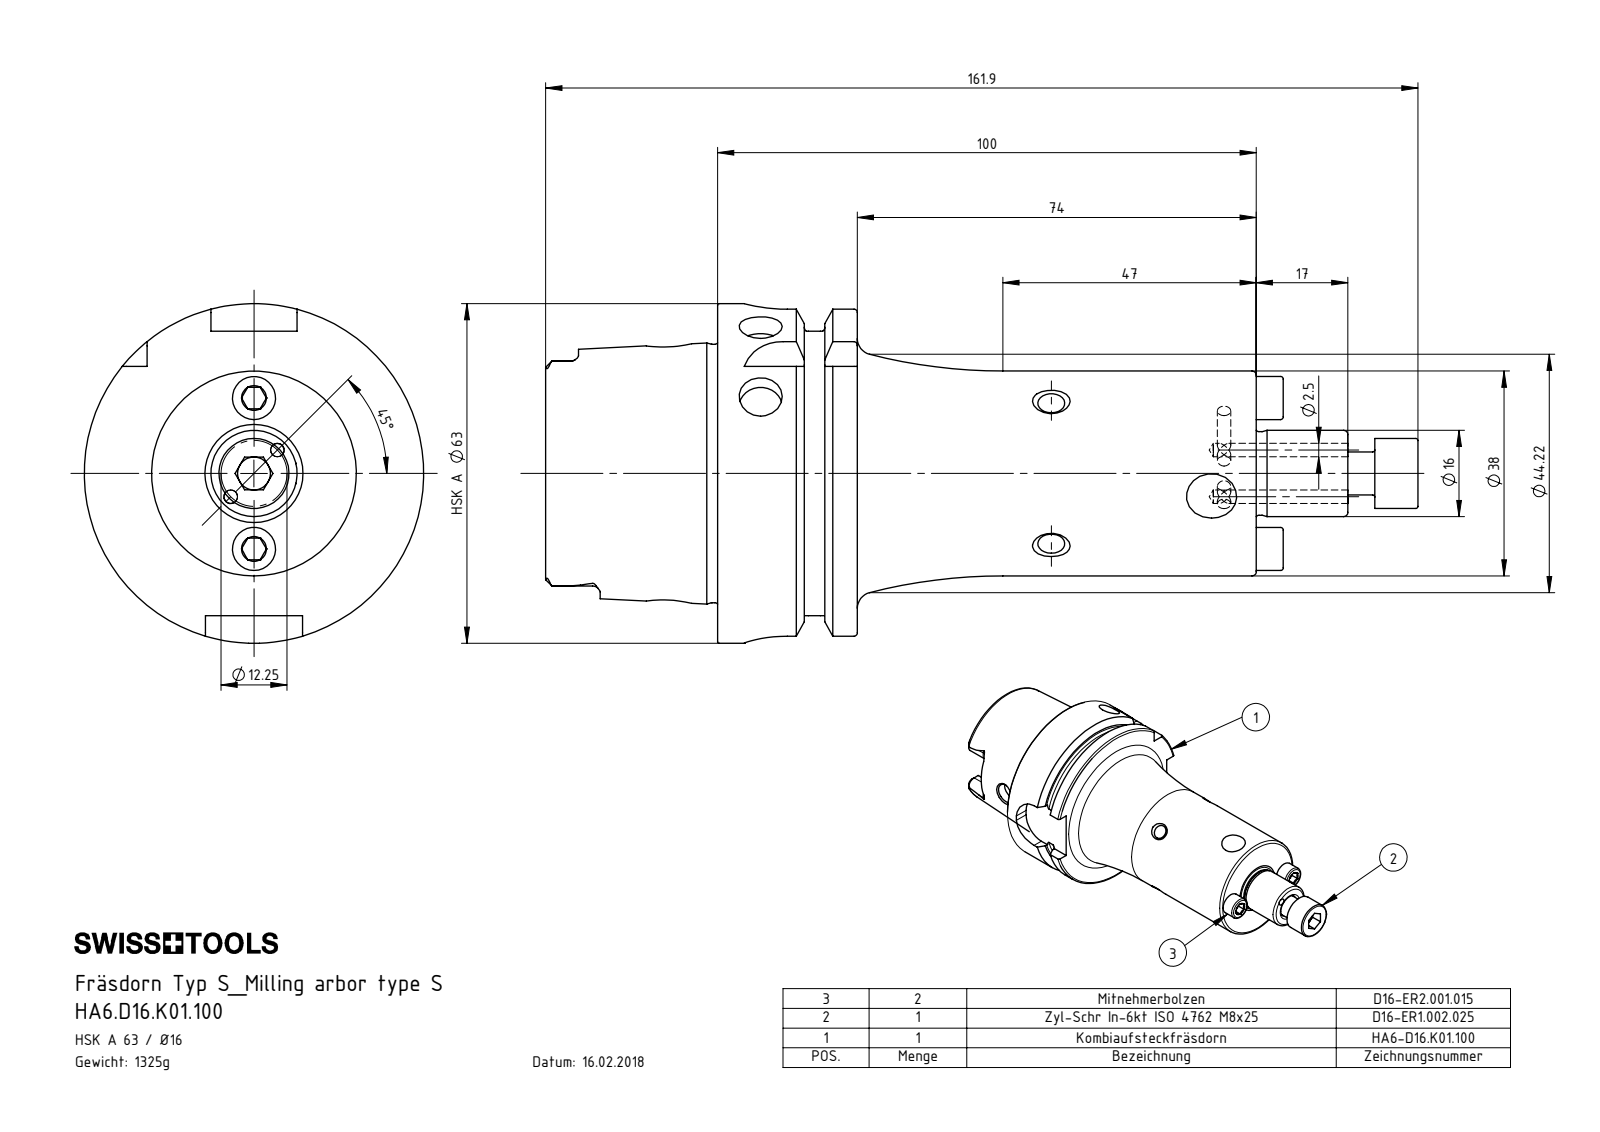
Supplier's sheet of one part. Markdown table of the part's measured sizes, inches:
| quantity | value |
| --- | --- |
| part name | D16-ER2.001.015_B; D16-ER1.002.025_A; HA6.D16.K01.100; HA6-D16.K01.100_C_Fertigbearbeitung |
| STEP written by | SolidWorks 2017 (CONFIG_CONTROL_DESIGN) |
| units | inches |
| bodies | 4 solids, 389 faces (91 planar, 111 cylindrical, 187 other) |
| overall size | 6.374 × 2.48 × 2.48 |
| volume | 10.3 in³ |
| surface area | 58.62 in² |
| round holes (diameter × count) | 0.098 × 3, 0.13 × 2, 0.197 × 2, 0.236 × 2, 0.315 × 2, 0.268 × 1, 0.295 × 1, 0.331 × 1, 0.335 × 1, 0.394 × 1, 0.669 × 1, 0.748 × 1 |
| round bosses / shafts (diameter × count) | 0.315 × 3, 0.157 × 2, 0.118 × 2, 2.48 × 1, 2.163 × 1, 1.887 × 1, 1.496 × 1, 0.63 × 1 |
| partial cylindrical surfaces (radius × count) | 0.055 × 6, 0.113 × 4, 0.315 × 4, 0.079 × 2 |
| main face-to-face distances | 1.022, 3.937, 2.915, 0.63, 0.392, 3.545, 1.256, 1.648, 2.278, 5.193 |
| hole center spacings | 0.241, 0.417, 0.551, 0.741, 0.482, 1.102, 1.262 |
